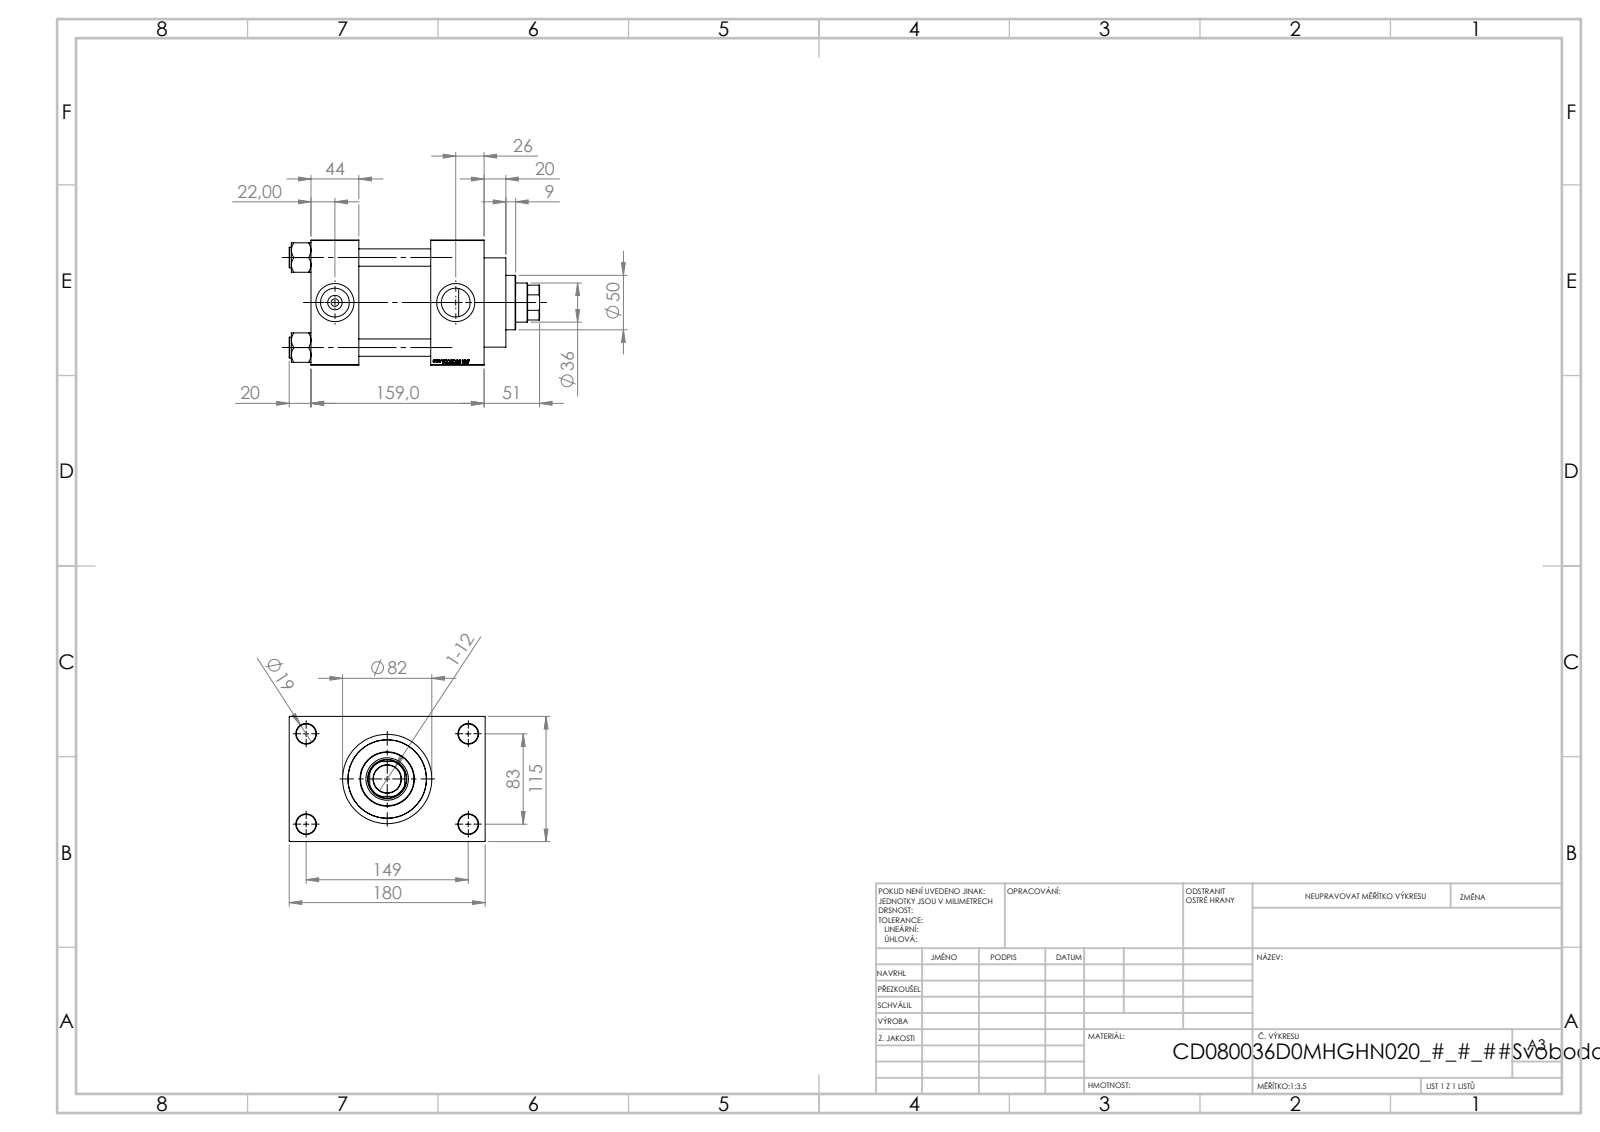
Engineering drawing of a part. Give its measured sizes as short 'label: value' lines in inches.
name: V215CD_VCP_D; V215CD_D_TYCINKA; V215CD_NUT_M5_D; V215CD_VC_A (+1 more)
written by: SolidWorks 2019 (CONFIG_CONTROL_DESIGN)
unit: in
bodies: 11 solids, 1151 faces (545 planar, 88 cylindrical, 518 other)
size: 9.055 × 7.087 × 4.528
volume: 120.8 in³; area: 459.7 in²
holes: 4× ⌀0.63, 4× ⌀0.709, 2× ⌀0.276, 2× ⌀1.041, 2× ⌀1.378, 1× ⌀1.004, 1× ⌀1.417, 1× ⌀1.535, 1× ⌀2.402, 1× ⌀2.835, 1× ⌀3.15
bosses: 4× ⌀0.748, 1× ⌀3.386, 1× ⌀3.228, 1× ⌀1.969
rounds: 1× R0.689
face distances: 4.528, 2.598, 4.331, 1.929, 1.732, 6.26, 1.28, 5.807, 0.787, 2.717
hole spacings: 1.305, 2.302, 3.256, 3.357, 3.513, 4.561, 5.607, 3.268
